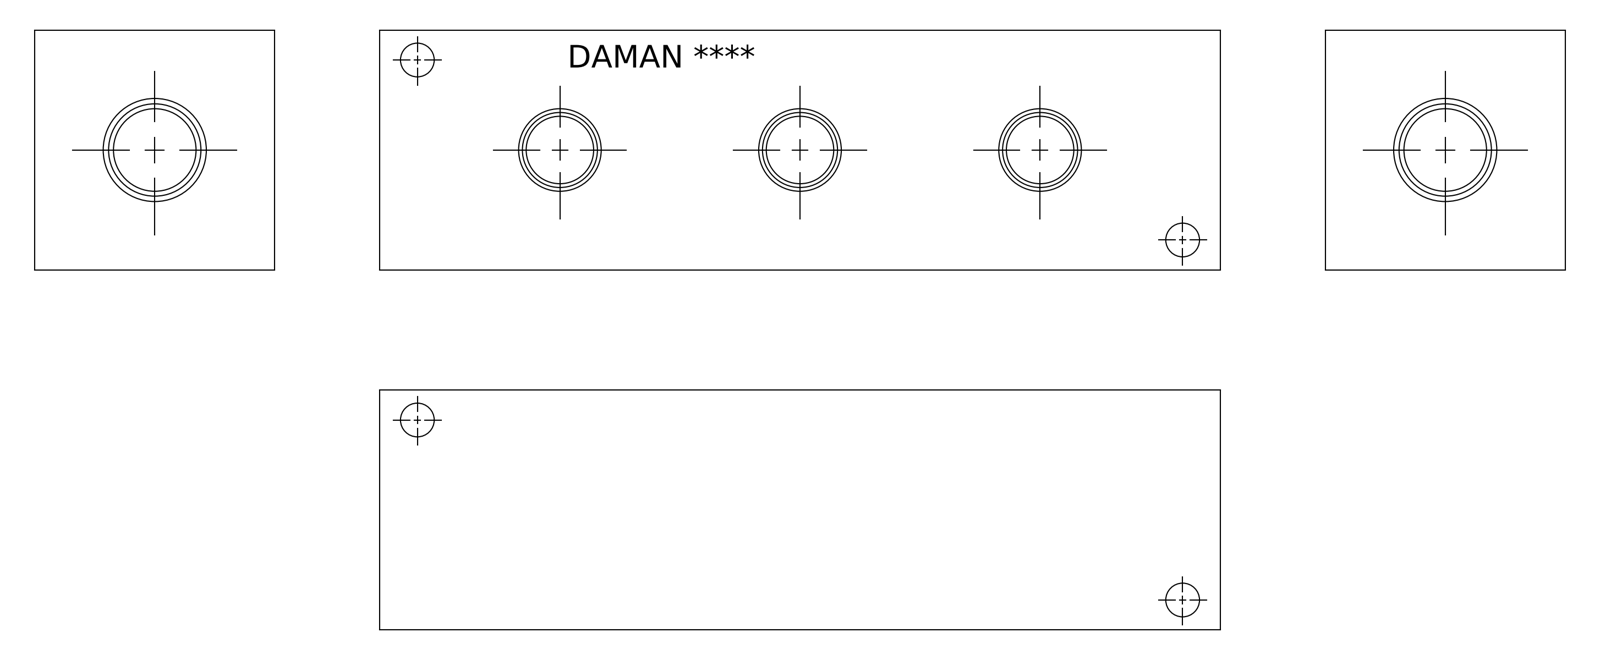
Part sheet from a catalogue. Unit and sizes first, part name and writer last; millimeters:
Units: millimetres
Overall size (bounding box): 177.8 × 50.8 × 50.8
Round holes (diameter × count): ⌀7.14 ×4, ⌀14.3 ×3, ⌀17.3 ×3, ⌀17.48 ×1, ⌀21.59 ×1
Main face-to-face distances: 50.8, 177.8, 15.37, 162.43, 39.07, 11.73, 147.06, 50.76, 11.69, 3.62
Hole centre spacings: 35.69, 50.8, 83.19, 133.15, 166.38, 101.6
Volume: 429 753 mm³ · Surface area: 49 394 mm²
Bodies: 1 solid, 348 faces (211 planar, 18 cylindrical, 119 other)
Part name (STEP PRODUCT): Part_+H0000306P_3D
STEP written by: Autodesk Inventor 2020 (AUTOMOTIVE_DESIGN)
